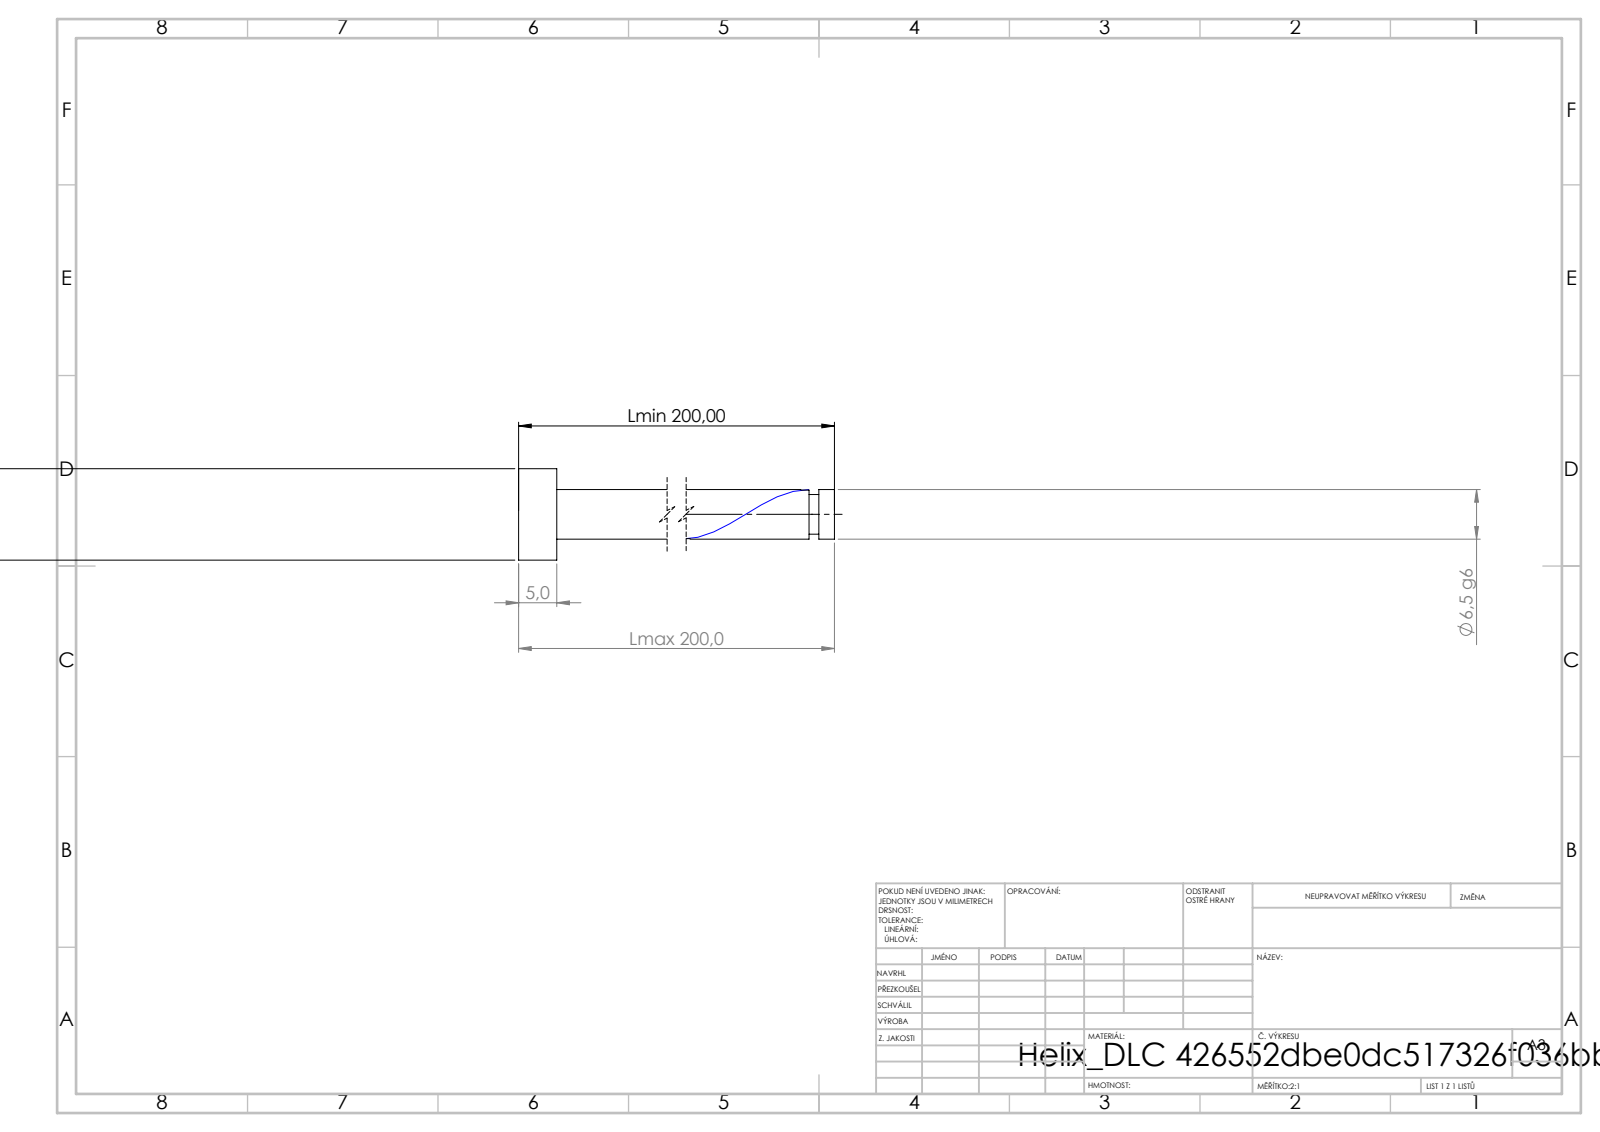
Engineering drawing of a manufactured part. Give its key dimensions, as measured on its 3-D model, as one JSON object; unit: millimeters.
{"step_written_by": "SolidWorks 2019 (CONFIG_CONTROL_DESIGN)", "units": "millimeters", "bodies": {"solids": 1, "faces": 21, "planar": 6, "cylindrical": 14, "other": 1}, "overall_size": [200, 12, 12], "volume_mm3": 6957, "surface_area_mm2": 4492, "round_bosses_or_shafts": [[12, 1], [6.5, 1], [5.2, 1]], "face_to_face_distances": [5, 200, 195, 197.96, 192.96, 2.04, 196.66, 191.66, 1.3, 3.34]}
